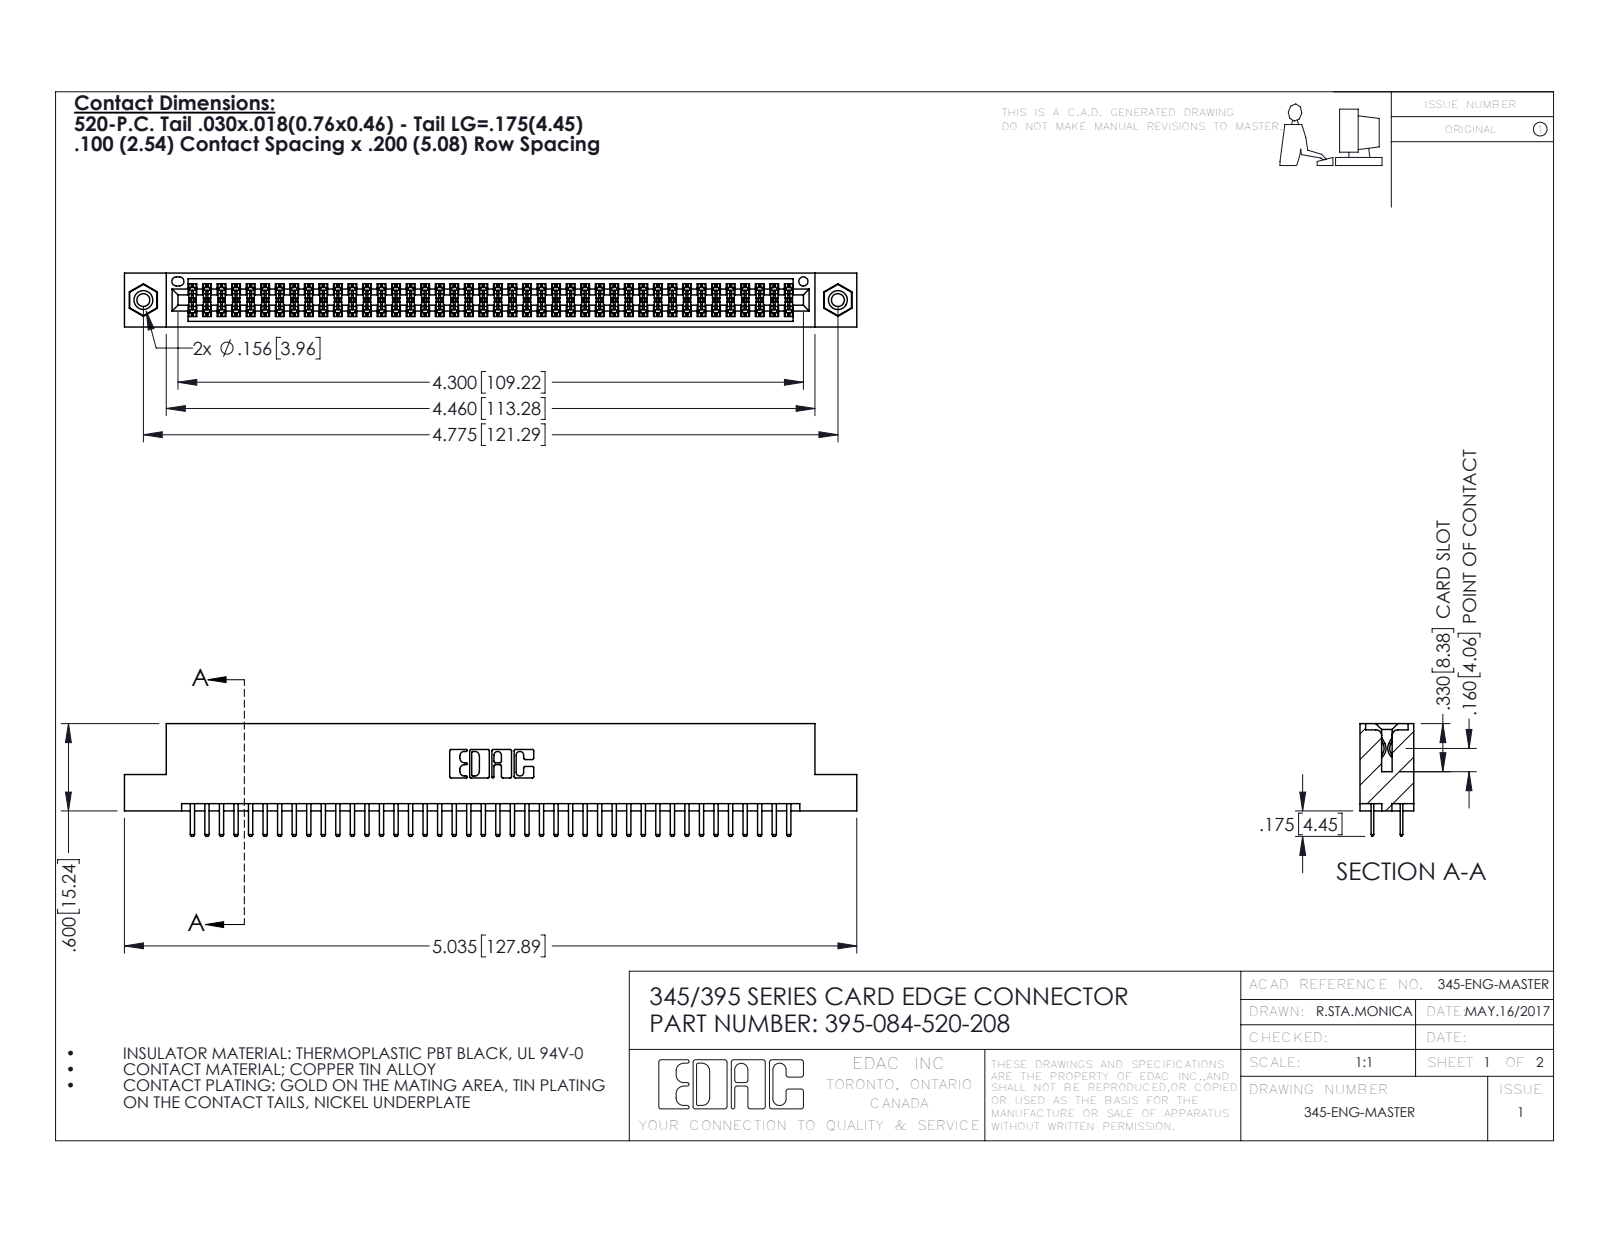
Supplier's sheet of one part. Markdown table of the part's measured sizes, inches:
| quantity | value |
| --- | --- |
| part name | 345 Part_Flush Mounting Lugs - 0.156 Dia-TI; 345-292-001_345-293-120; 345-250-001_345-250-003-102; 395-084-520-208 |
| STEP written by | SolidWorks 2016 (CONFIG_CONTROL_DESIGN) |
| units | inches |
| bodies | 87 solids, 4722 faces (3052 planar, 1654 cylindrical, 16 other) |
| overall size | 5.035 × 0.775 × 0.37 |
| volume | 0.755 in³ |
| surface area | 28.26 in² |
| round holes (diameter × count) | 0.089 × 2, 0.125 × 2, 0.156 × 2, 0.064 × 1 |
| round bosses / shafts (diameter × count) | 0.155 × 2 |
| partial cylindrical surfaces (radius × count) | 0.006 × 126, 0.01 × 88, 0.01 × 22, 0.007 × 6, 0.031 × 6, 0.026 × 3, 0.014 × 2, 0.019 × 2 |
| main face-to-face distances | 0.072, 0.298, 0.2, 0.37, 0.098, 0.272, 0.025, 0.225, 0.022, 0.072 |
| hole center spacings | 0.27, 4.539, 4.775 |
